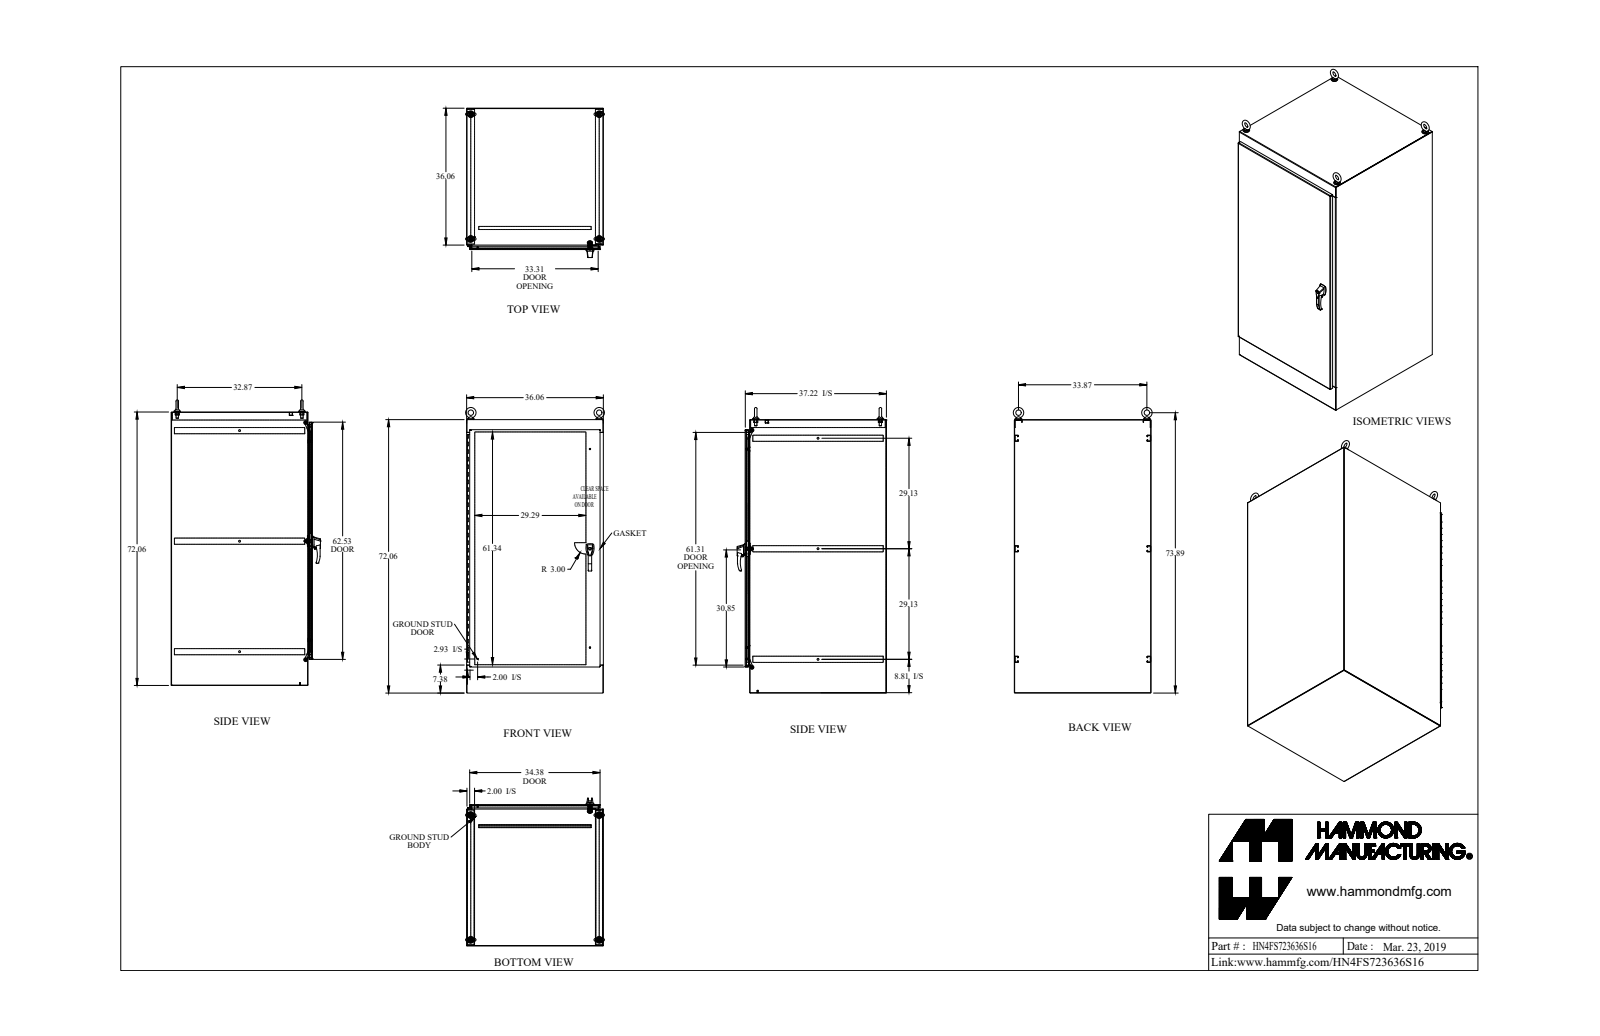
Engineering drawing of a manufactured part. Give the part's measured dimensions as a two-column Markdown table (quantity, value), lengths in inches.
| quantity | value |
| --- | --- |
| part name | HN4FS723636S16 |
| STEP written by | SolidWorks 2018 (AUTOMOTIVE_DESIGN) |
| units | inches |
| bodies | 65 solids, 2016 faces (905 planar, 886 cylindrical, 225 other) |
| overall size | 75.489 × 39.362 × 36.604 |
| volume | 1 475 in³ |
| surface area | 30 884 in² |
| round holes (diameter × count) | 0.304 × 10, 0.35 × 7, 0.75 × 6, 0.527 × 4, 0.625 × 4, 0.68 × 4, 0.5 × 3, 0.25 × 2, 0.257 × 2, 0.28 × 2, 0.281 × 2, 0.313 × 2 |
| round bosses / shafts (diameter × count) | 1.75 × 4, 1.5 × 4, 1.25 × 4, 0.738 × 4, 1 × 2, 0.75 × 2, 0.63 × 2, 0.625 × 2 |
| partial cylindrical surfaces (radius × count) | 0.043 × 42, 0.138 × 36, 0.5 × 23, 0.125 × 22, 0.018 × 16, 0.06 × 15, 0.048 × 13, 0.143 × 13 |
| main face-to-face distances | 0.095, 35.965, 37.152, 35.87, 36.06, 71.965, 37.057, 37.247, 71.87, 72.06 |
| hole center spacings | 6, 12, 18, 24, 30, 33.87, 36, 42 |
